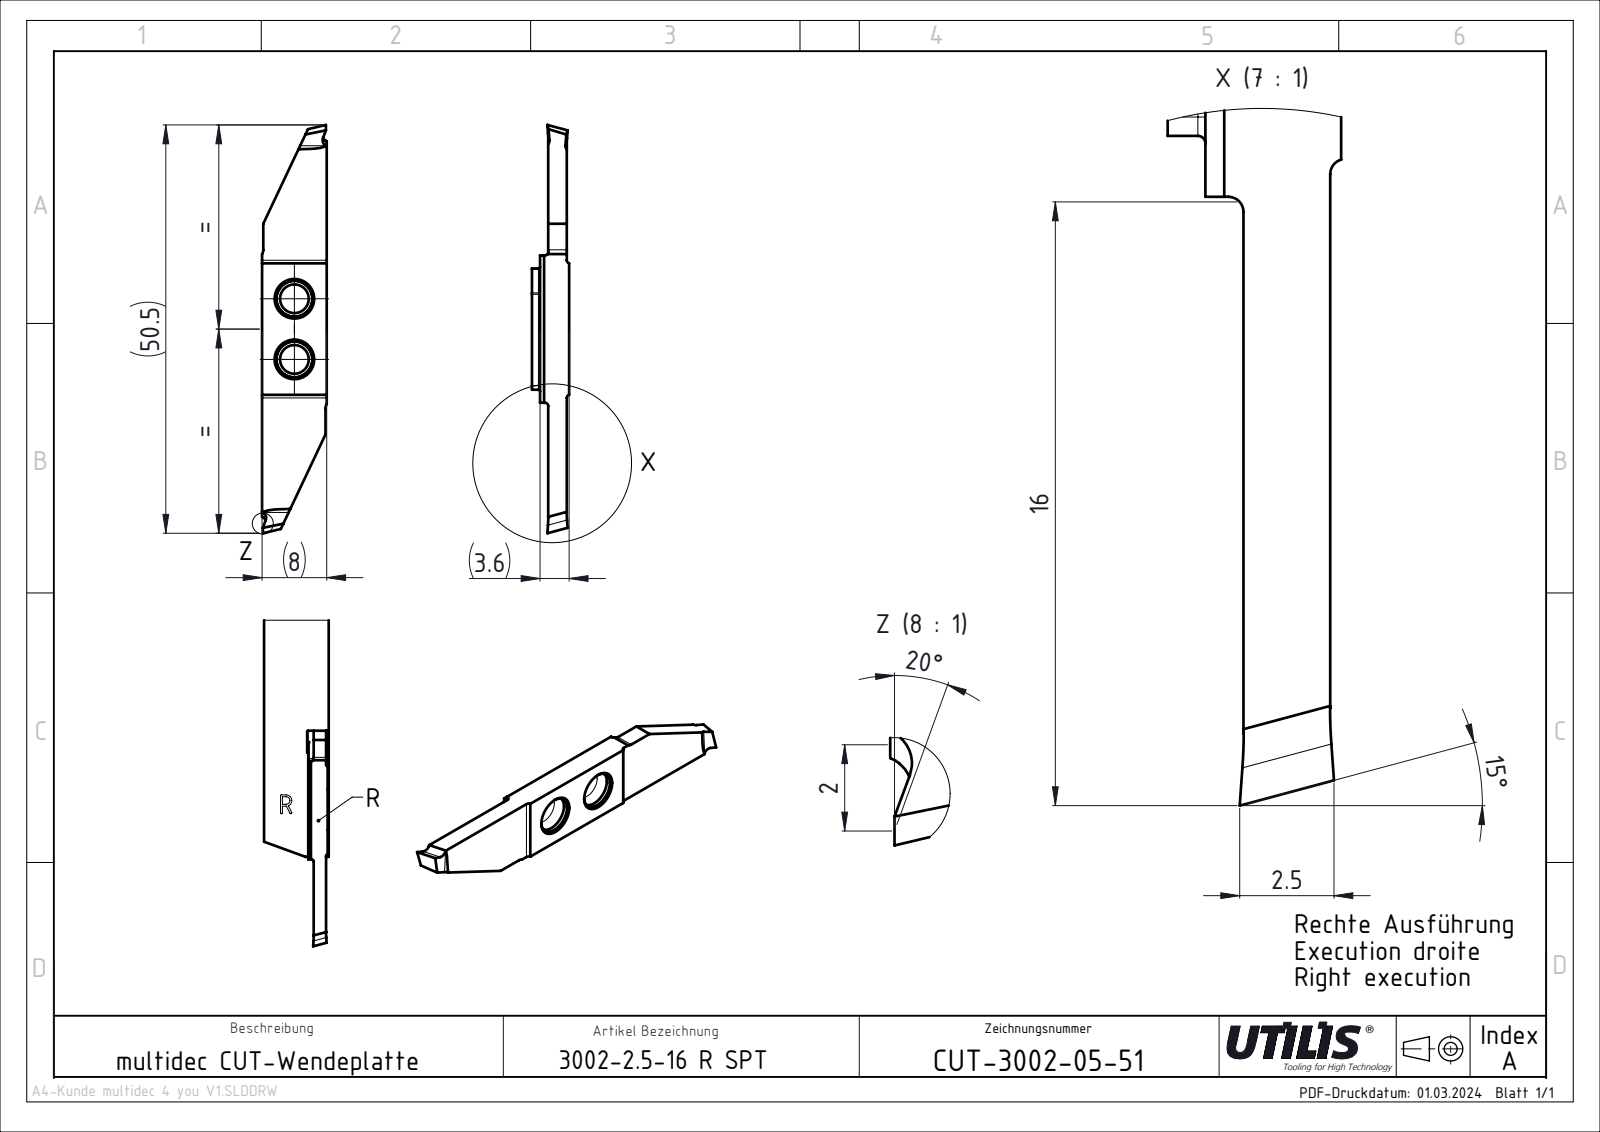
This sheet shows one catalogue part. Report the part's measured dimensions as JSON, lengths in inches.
{"part_name": "CUT-3002 SPT Slim_and_Deep; ASME Y14.5", "step_written_by": "SolidWorks 2023 SP4 || FormatWorks Professional (AP242_MANAGED_MODEL_BASED_3D_ENGINEERING_MIM_LF)", "units": "inches", "bodies": {"solids": 1, "faces": 32, "planar": 22, "cylindrical": 10, "other": 0}, "overall_size": [1.988, 0.315, 0.142], "volume_in3": 0.053, "surface_area_in2": 1.54, "round_holes": [[0.14, 2]], "partial_cylinders_radius": [[0.016, 4], [0.039, 2]], "face_to_face_distances": [0.091, 0.102, 0.04, 0.13, 0.142, 0.315, 0.712, 0.309, 0.303, 0.717], "hole_center_spacings": [0.295]}
